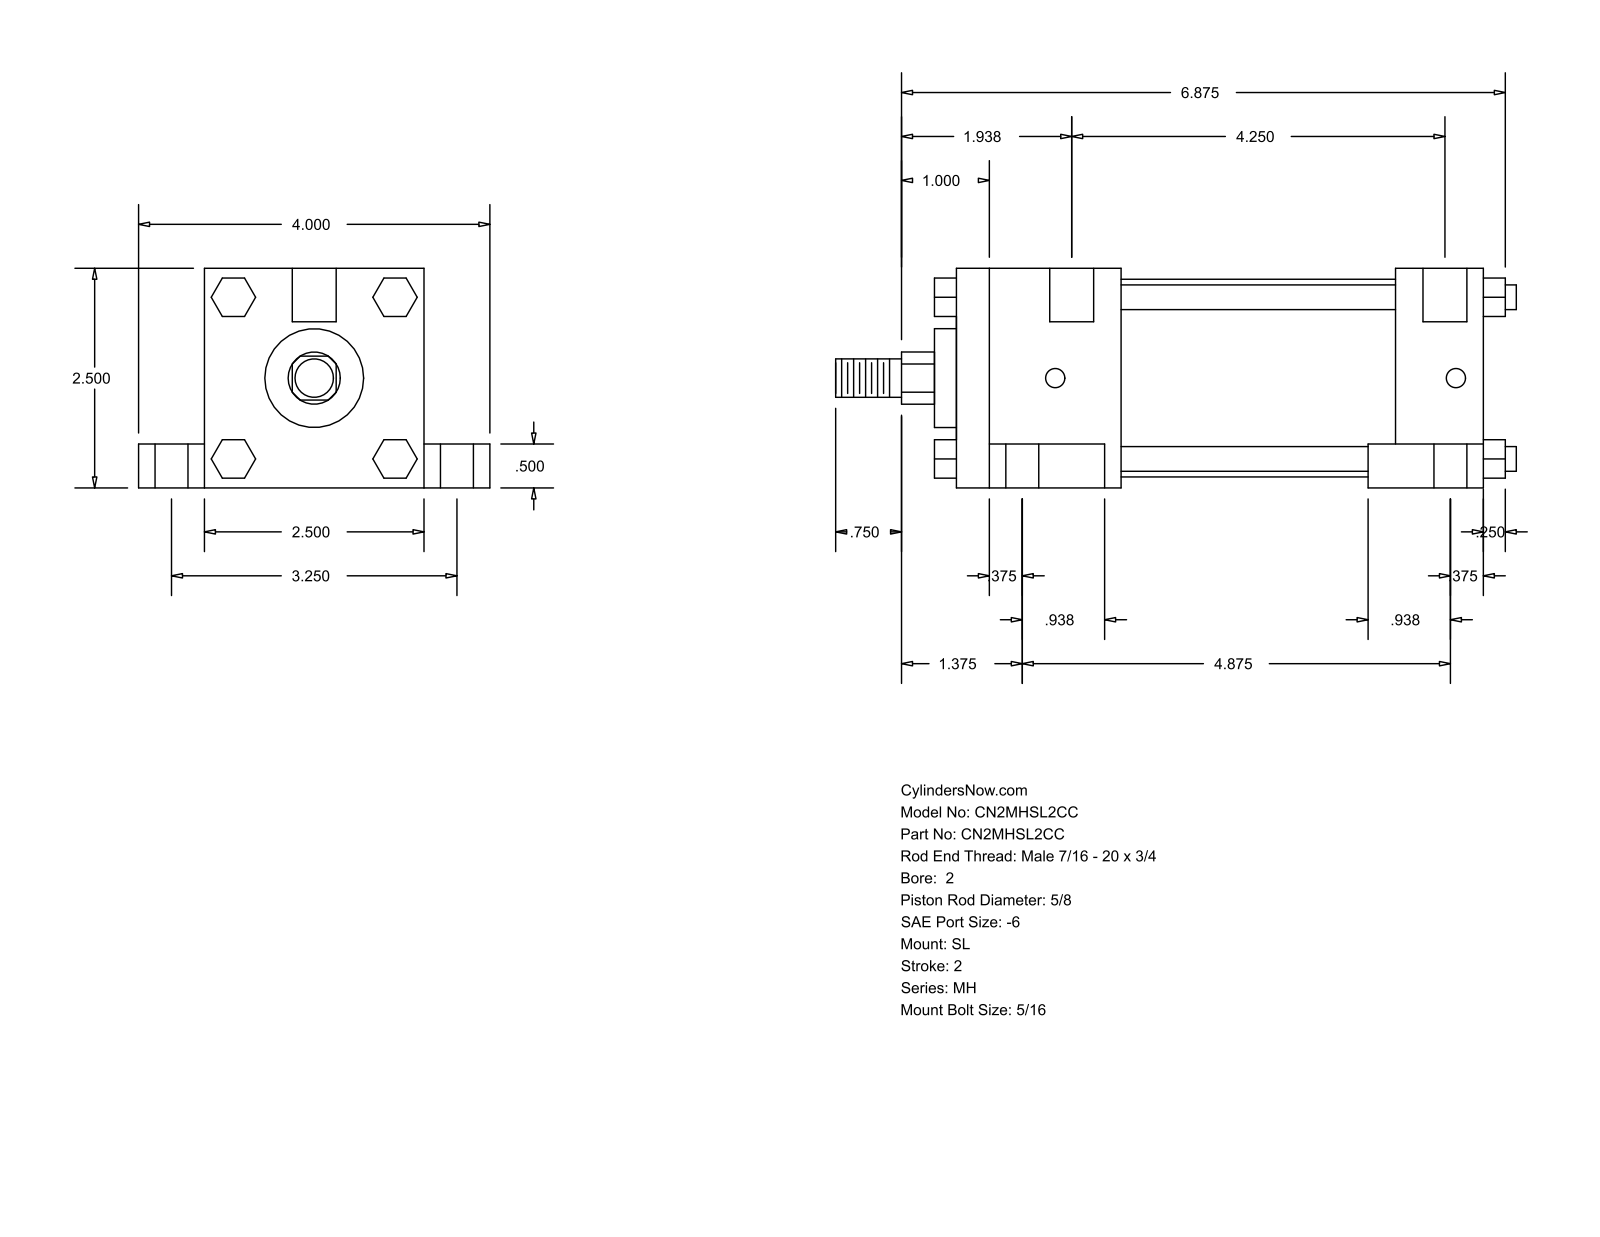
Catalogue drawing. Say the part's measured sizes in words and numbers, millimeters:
The part is named "MH_SL__0200_0.625". Its 3-D file was written by "GSSL Pune (CONFIG_CONTROL_DESIGN)". It is 0 solids with 148 faces: 112 planar, 36 cylindrical and 0 other. Overall it measures 196.85 by 101.6 by 63.5 millimeters. Round holes: 4 of diameter 5.56, 4 of diameter 9.53, 4 of diameter 15.88, 2 of diameter 12.7. Round bosses or shafts: 4 of diameter 7.14, 1 of diameter 57.15, 1 of diameter 28.57, 1 of diameter 15.88, 1 of diameter 11.11. Partial cylindrical surfaces (rounded edges, fillets, slot ends): 1 of radius 7.54. The main face-to-face distances are 63.5, 152.4, 12.7, 19.05, 82.55, 50.8, 25.4, 127, 47.62, 79.38. The hole center spacings are 41.3, 42.36, 43.67, 82.54, 115.89, 117.06, 121.52, 123.83.
